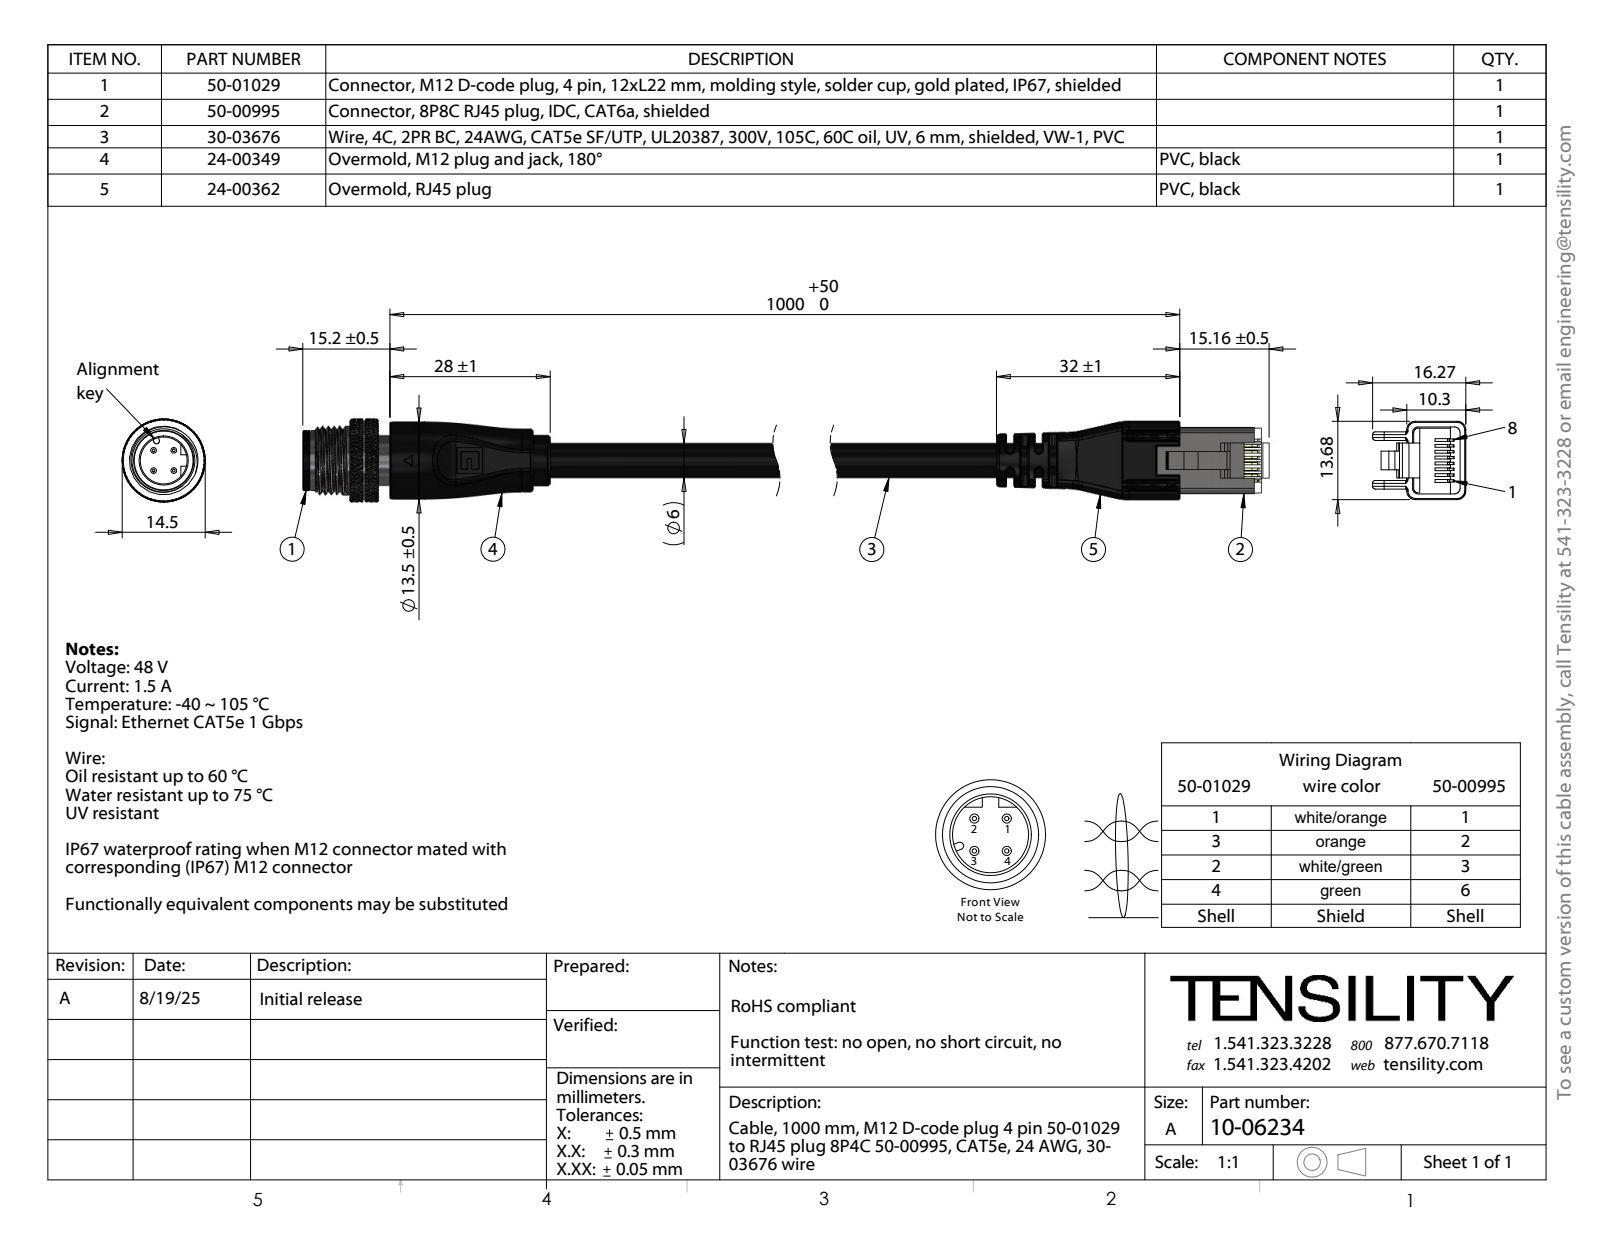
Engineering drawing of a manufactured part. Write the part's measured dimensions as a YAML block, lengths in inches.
part_name: "50-01029-01_默认; 50-01029-03_默认; 24-00362; 24-00349_Mexico (+6 more)"
step_written_by: "SolidWorks 2025 (CONFIG_CONTROL_DESIGN)"
units: inches
bodies: {solids: 54, faces: 3209, planar: 470, cylindrical: 811, other: 1928}
overall_size: [9.067, 0.723, 0.571]
volume: 0.849
surface_area: 45.15
round_holes:
  - {diameter: 0.008, count: 28}
  - {diameter: 0.039, count: 4}
  - {diameter: 0.041, count: 4}
  - {diameter: 0.124, count: 1}
  - {diameter: 0.126, count: 1}
  - {diameter: 0.14, count: 1}
  - {diameter: 0.315, count: 1}
  - {diameter: 0.323, count: 1}
  - {diameter: 0.346, count: 1}
  - {diameter: 0.374, count: 1}
round_bosses_or_shafts:
  - {diameter: 0.055, count: 4}
  - {diameter: 0.571, count: 1}
  - {diameter: 0.547, count: 1}
  - {diameter: 0.531, count: 1}
  - {diameter: 0.472, count: 1}
  - {diameter: 0.433, count: 1}
  - {diameter: 0.413, count: 1}
  - {diameter: 0.366, count: 1}
partial_cylinders:
  - {radius: 0.008, count: 11}
  - {radius: 0.02, count: 10}
  - {radius: 0.059, count: 10}
  - {radius: 0.024, count: 8}
  - {radius: 0.039, count: 5}
  - {radius: 0.394, count: 4}
  - {radius: 0.031, count: 2}
  - {radius: 0.045, count: 2}
face_to_face_distances: [0.049, 0.098, 0.039, 0.148, 0.197, 0.366, 0.276, 7.854, 0.499, 0.46]
hole_center_spacings: [0.042, 0.075, 0.082, 0.014, 0.043, 0.067, 0.071, 0.089]
